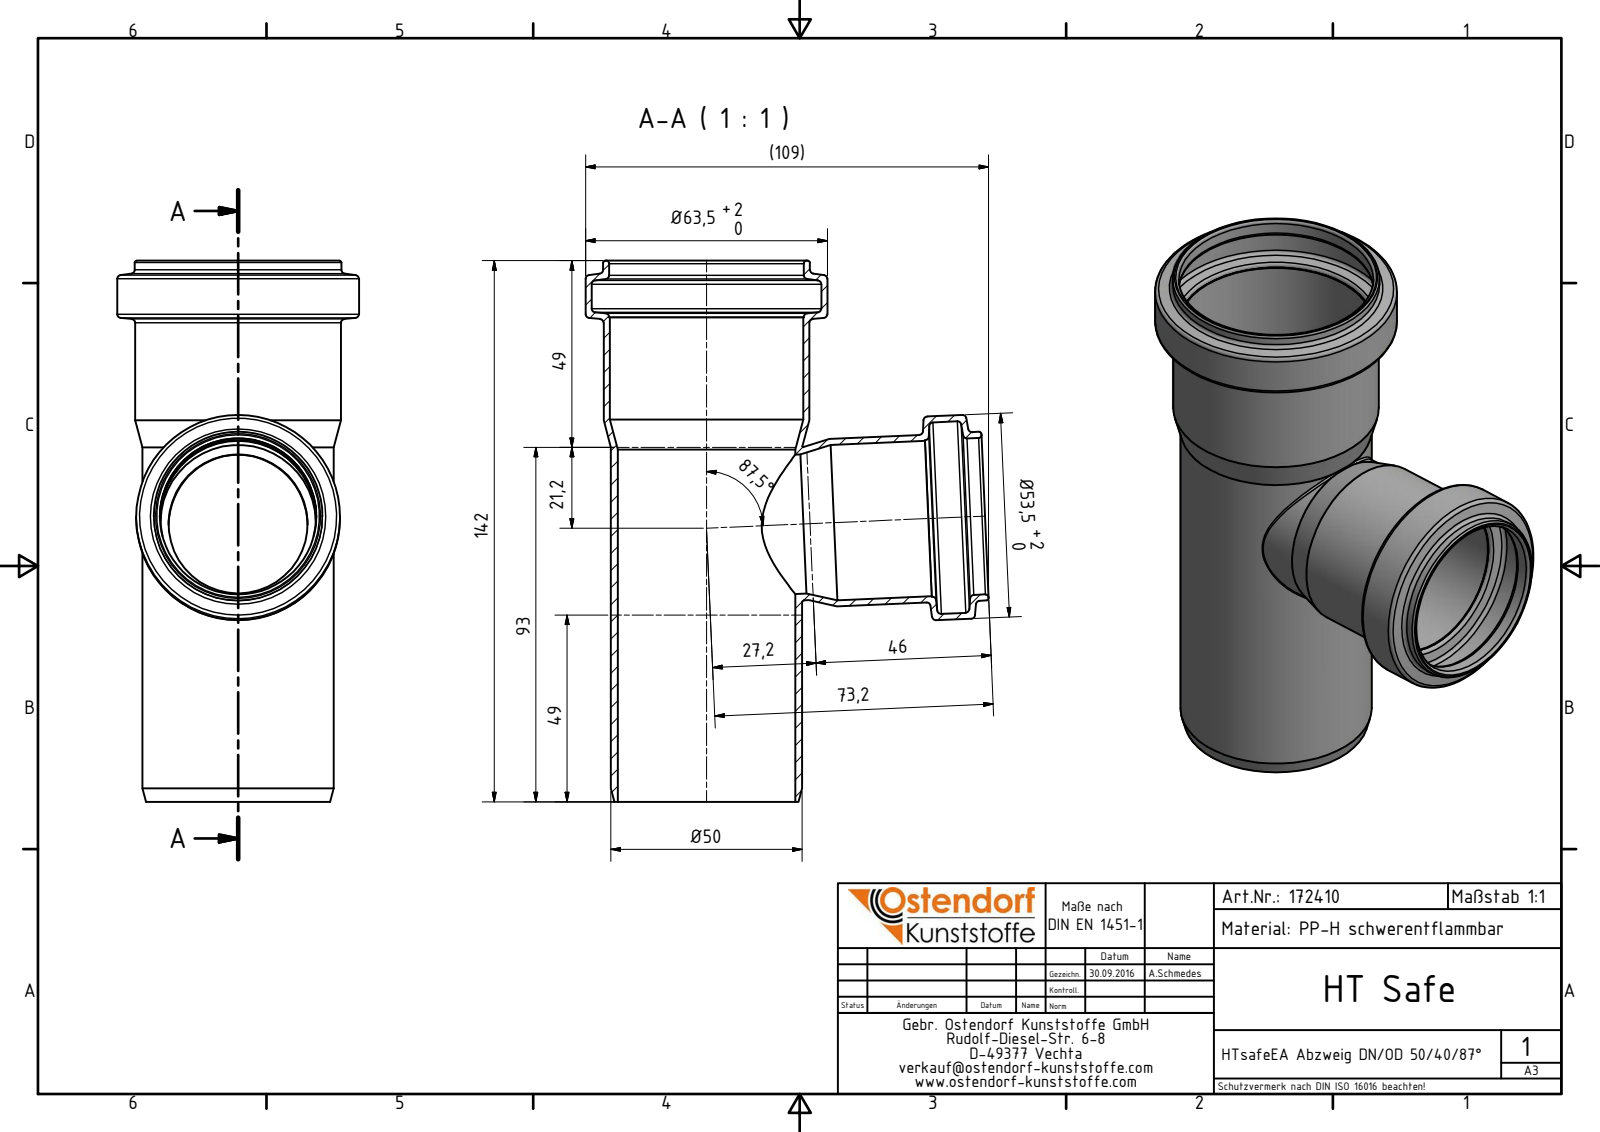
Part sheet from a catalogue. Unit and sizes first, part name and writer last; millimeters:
Units: millimetres
Overall size (bounding box): 142 × 105.83 × 63.5
Round holes (diameter × count): ⌀41.1 ×2, ⌀36.5 ×1, ⌀40.8 ×1, ⌀46.6 ×1, ⌀50.3 ×1, ⌀50.8 ×1, ⌀51.1 ×1, ⌀60.3 ×1
Round bosses / shafts (diameter × count): ⌀63.5 ×1, ⌀54.3 ×1, ⌀54 ×1, ⌀53.5 ×1, ⌀50.2 ×1, ⌀44.3 ×1, ⌀44 ×1, ⌀40.1 ×1
Main face-to-face distances: 142, 14.9, 127.1
Volume: 52 478 mm³ · Surface area: 62 207 mm²
Bodies: 1 solid, 57 faces (5 planar, 18 cylindrical, 34 other)
Part name (STEP PRODUCT): 172410 HTsafeEA DN_OD 50_40_87°
STEP written by: Autodesk Inventor 2016 (AUTOMOTIVE_DESIGN)
